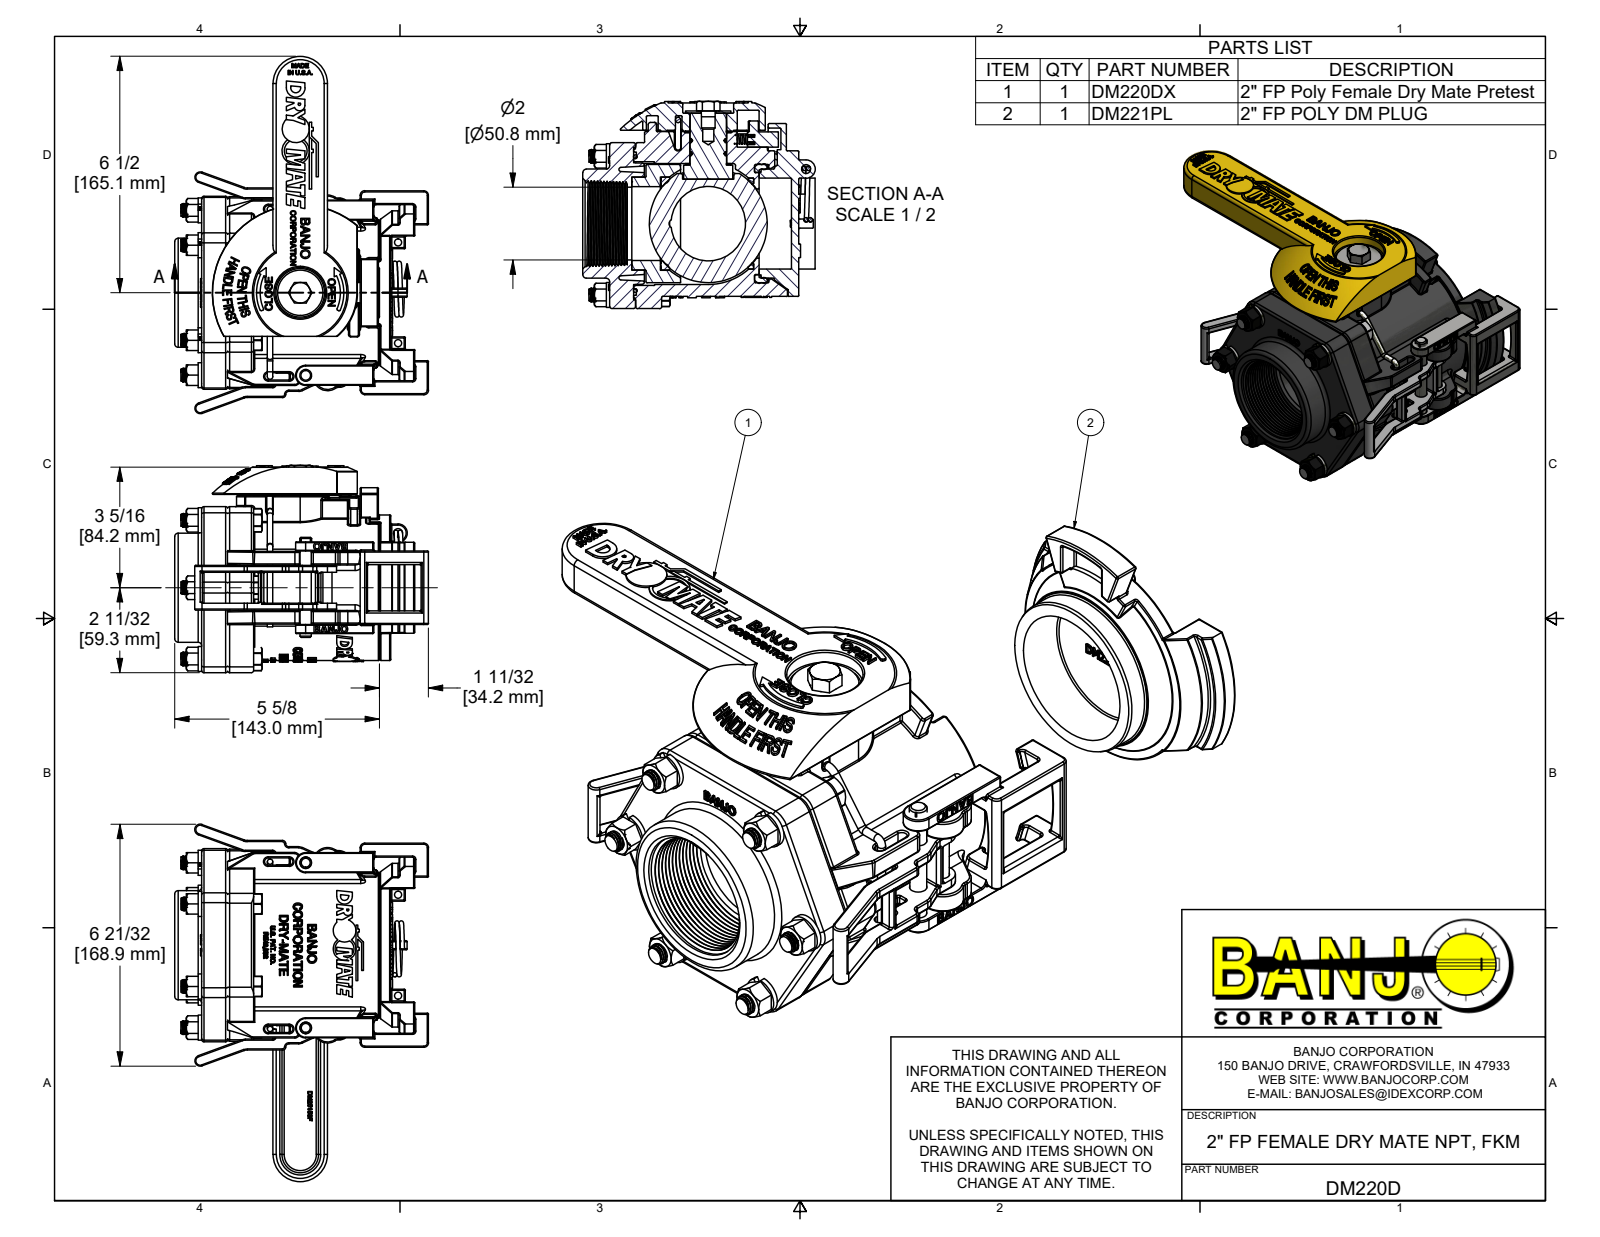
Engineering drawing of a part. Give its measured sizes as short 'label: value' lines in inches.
name: DM220D; DM220DX; DM25254F; DM25254FY (+8 more)
written by: Autodesk Inventor 2022 (AUTOMOTIVE_DESIGN)
unit: in
bodies: 49 solids, 7080 faces (2474 planar, 1821 cylindrical, 2785 other)
size: 9.825 × 6.975 × 5.698
volume: 76.81 in³; area: 614 in²
holes: 7× ⌀0.406, 6× ⌀0.307, 6× ⌀0.385, 6× ⌀0.45, 3× ⌀0.25, 2× ⌀0.2, 2× ⌀0.313, 2× ⌀0.32, 2× ⌀2.05, 1× ⌀0.307, 1× ⌀0.417, 1× ⌀0.59
bosses: 90× ⌀0.324, 8× ⌀0.15, 7× ⌀0.375, 6× ⌀0.687, 2× ⌀0.325, 2× ⌀0.311, 2× ⌀0.26, 1× ⌀4.1
rounds: 436× R0.03, 103× R0.06, 51× R0.01, 50× R0.02, 19× R0.125, 15× R0.313, 14× R0.25, 12× R0.062
face distances: 5.2, 0.66, 0.25, 4.54, 0.05, 0.71, 0.72, 0.5, 1.25, 2.01
hole spacings: 0.601, 2.085, 2.144, 2.263, 2.264, 2.265, 2.266, 2.275
